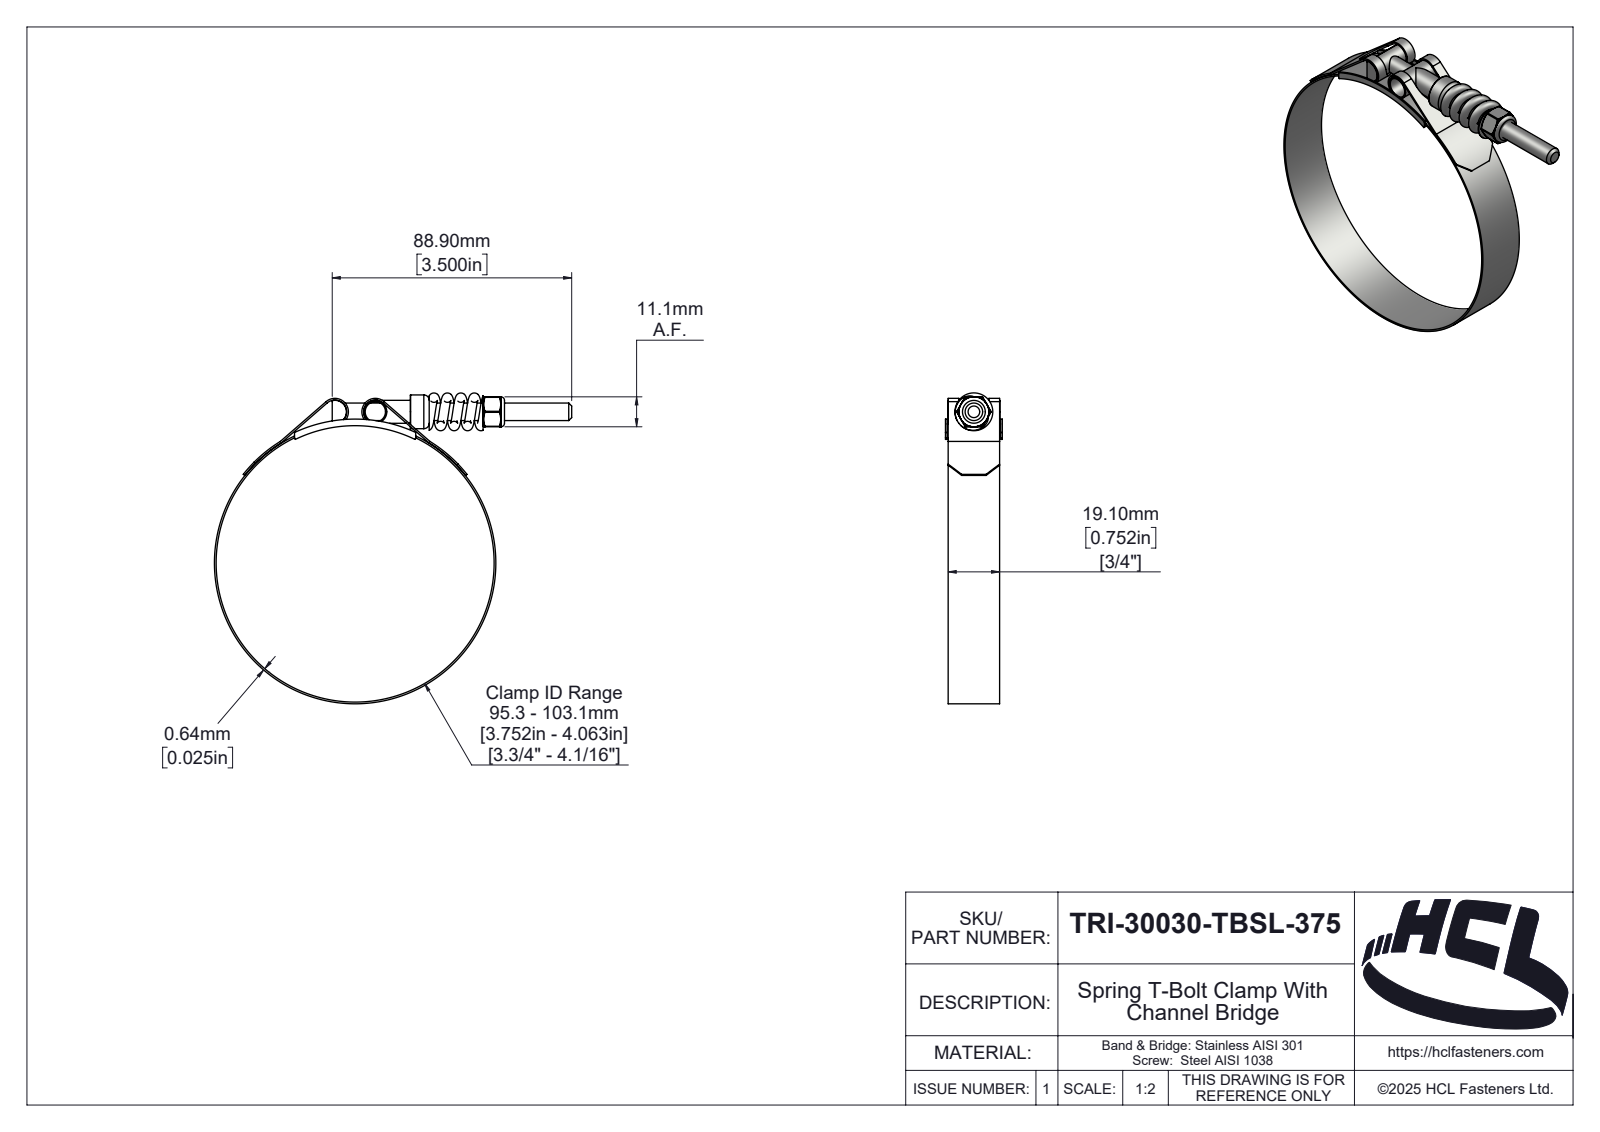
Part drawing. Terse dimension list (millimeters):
name: TRI-30030-TBSL-375
written by: SolidWorks 2025 (AUTOMOTIVE_DESIGN)
unit: mm
bodies: 7 solids, 332 faces (48 planar, 122 cylindrical, 162 other)
size: 133.64 × 115.36 × 21.1
volume: 12 038 mm³; area: 24 822 mm²
holes: 1× ⌀5.4, 1× ⌀6.35, 1× ⌀6.5, 1× ⌀7.52, 1× ⌀103.2
bosses: 2× ⌀8.52, 1× ⌀104.48, 1× ⌀12.52
rounds: 6× R0.39, 2× R0.5, 2× R4.36, 2× R5, 1× R0.59, 1× R2.42, 1× R3.03, 1× R3.19
face distances: 0.64, 19.1, 1, 20.1, 20.46, 0.36, 19.46, 56, 21.1, 11.12
hole spacings: 56.6
